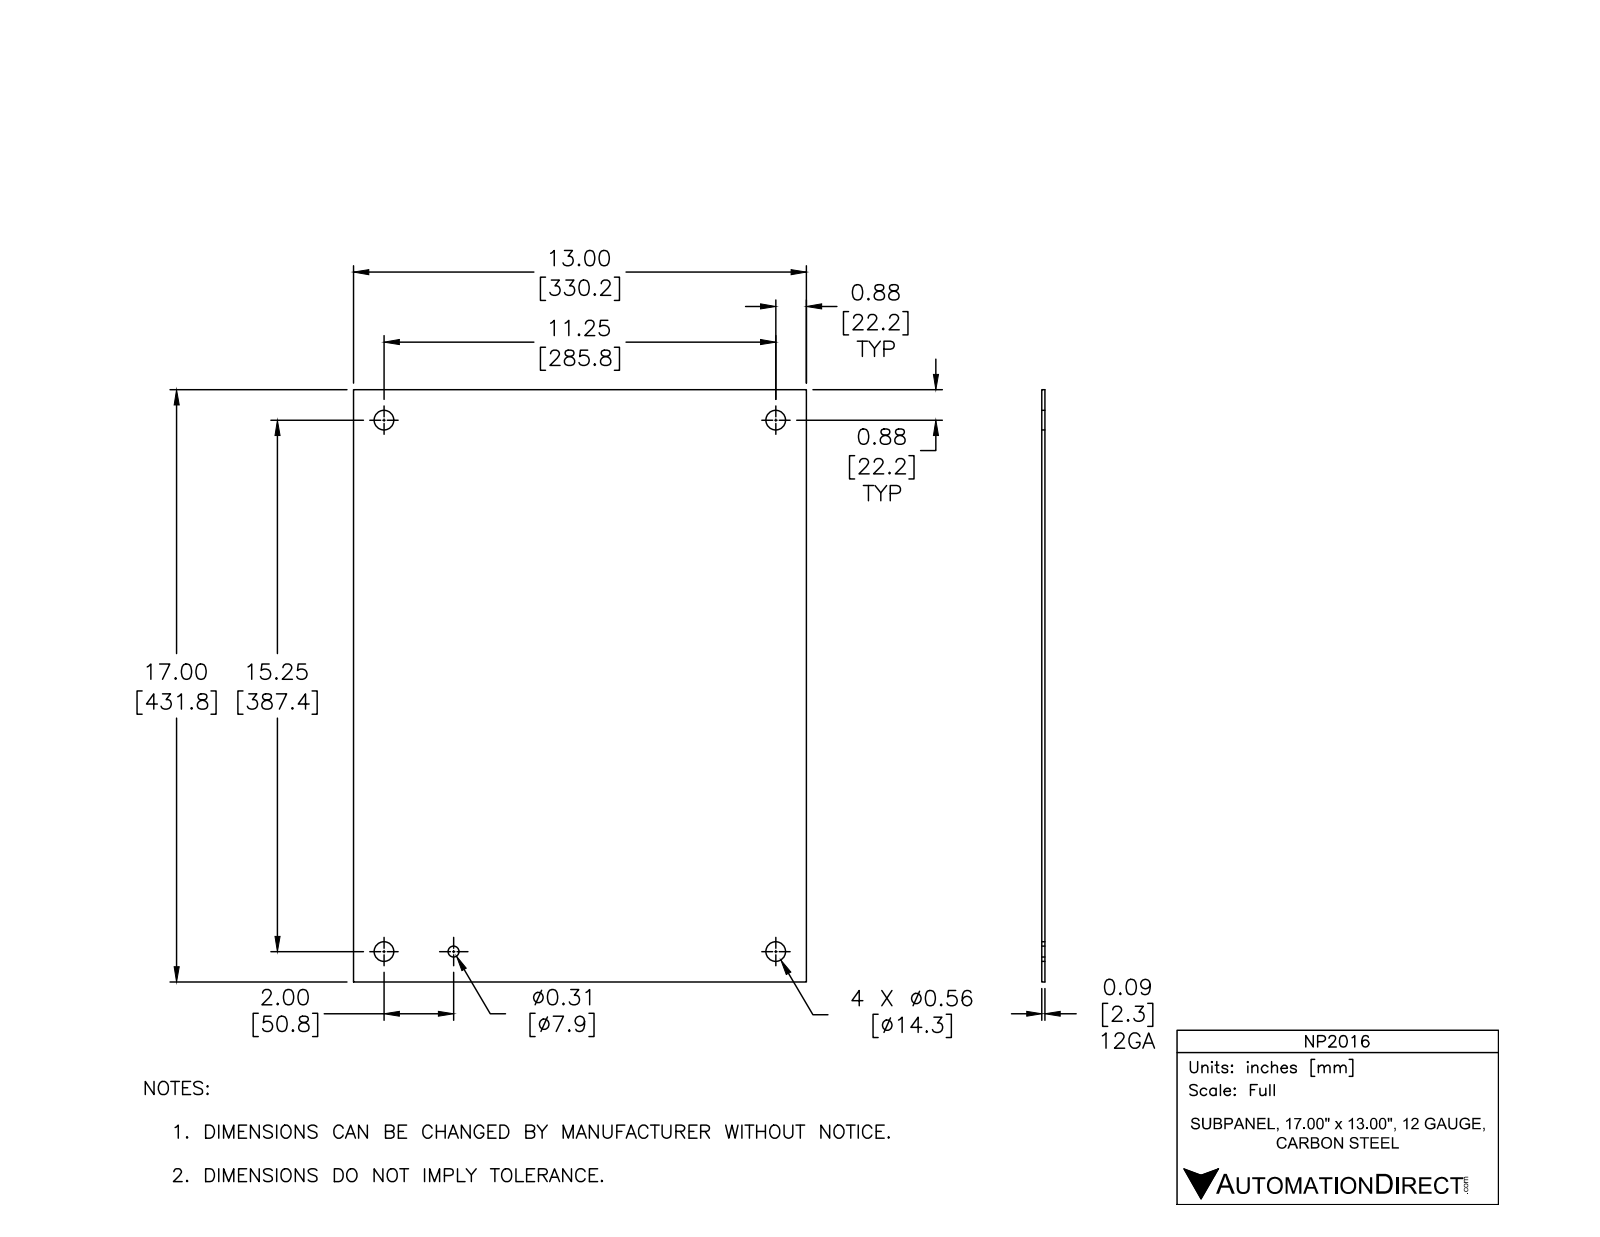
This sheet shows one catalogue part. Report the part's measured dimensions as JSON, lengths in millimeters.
{"part_name": "NP2016", "step_written_by": "Autodesk Inventor 2012 (AUTOMOTIVE_DESIGN)", "units": "millimeters", "bodies": {"solids": 1, "faces": 11, "planar": 6, "cylindrical": 5, "other": 0}, "overall_size": [431.8, 330.2, 2.4], "volume_mm3": 337900, "surface_area_mm2": 287900, "round_holes": [[14.3, 4], [7.9, 1]], "face_to_face_distances": [2.4, 330.2, 431.8], "hole_center_spacings": [285.8, 50.8, 235, 387.4, 387.4, 390.7, 453, 481.4]}
